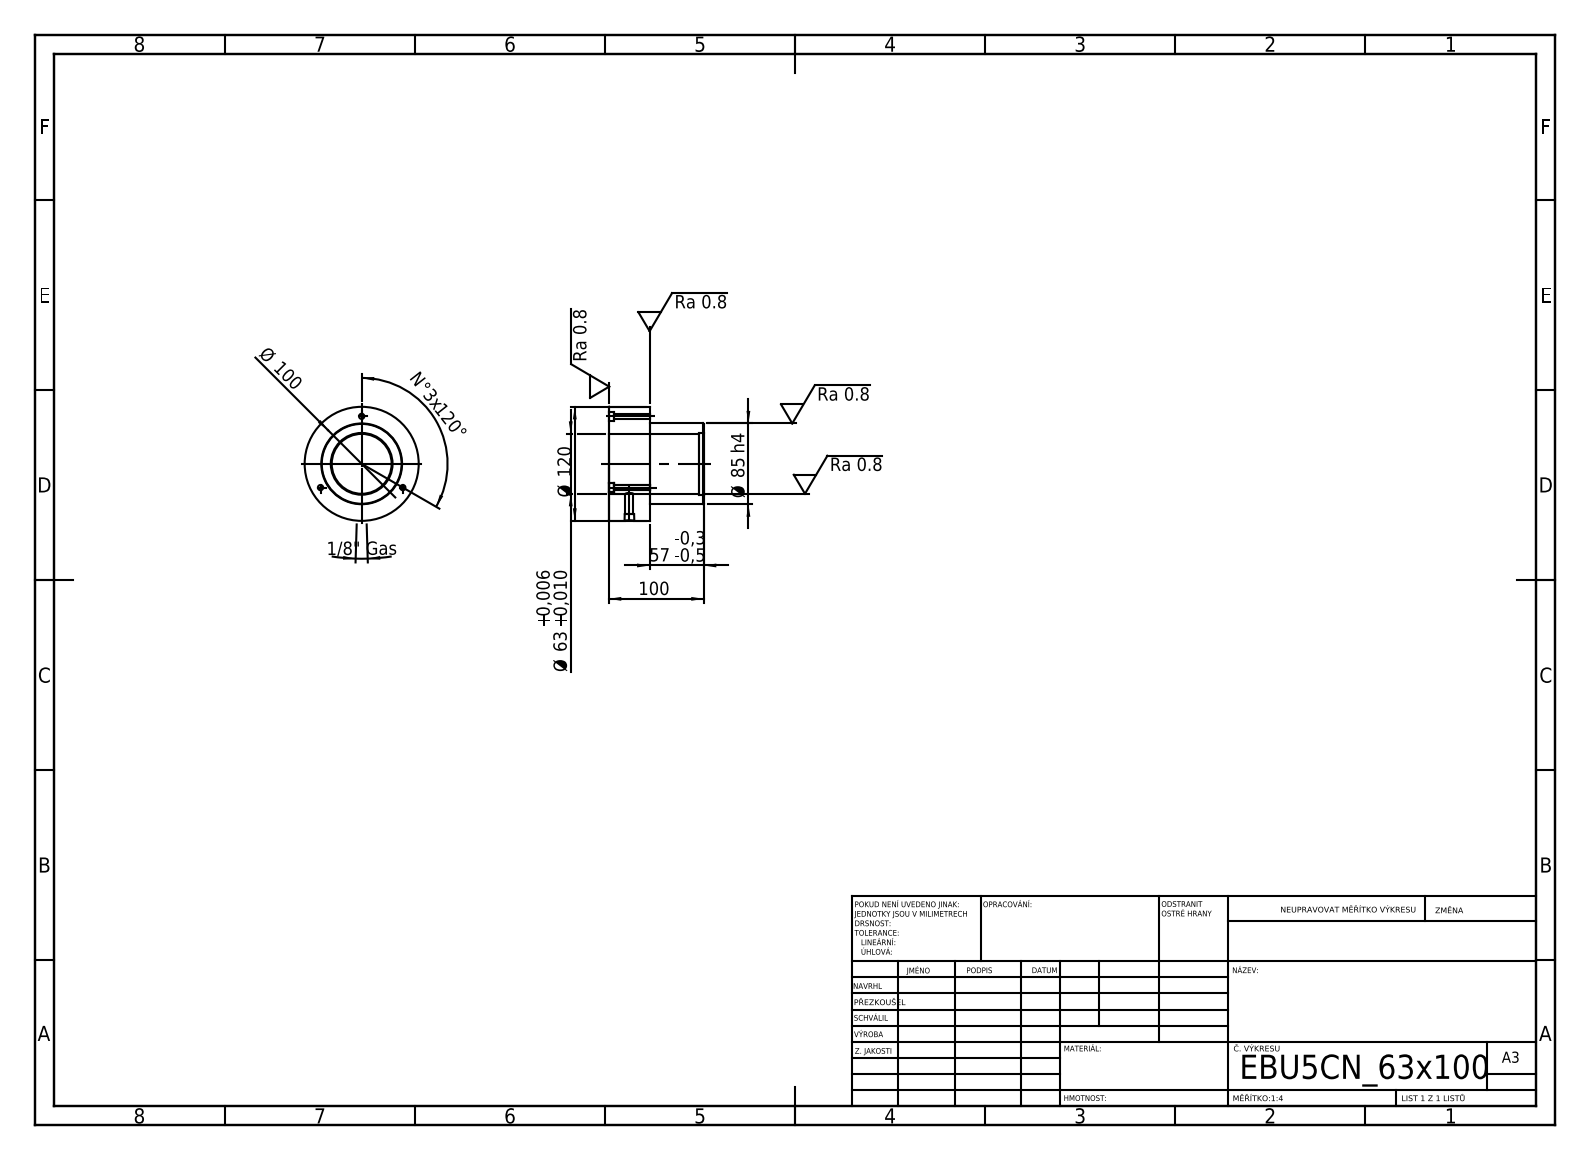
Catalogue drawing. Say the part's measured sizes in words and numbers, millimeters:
Its 3-D file was written by "SolidWorks 2019 (CONFIG_CONTROL_DESIGN)". It is 1 solid with 36 faces: 8 planar, 22 cylindrical and 6 other. Overall it measures 120 by 120 by 100 millimeters. Its volume is 491 244 cubic millimeters and its surface area 70 439 square millimeters. Round holes: 3 of diameter 5.5, 3 of diameter 10, 1 of diameter 8.43, 1 of diameter 63, 1 of diameter 65. Round bosses or shafts: 1 of diameter 120, 1 of diameter 85. The main face-to-face distances are 43, 57, 100, 5, 52, 95, 94.6, 89.6, 37.6, 5.4. The hole center spacings are 50, 86.6.
